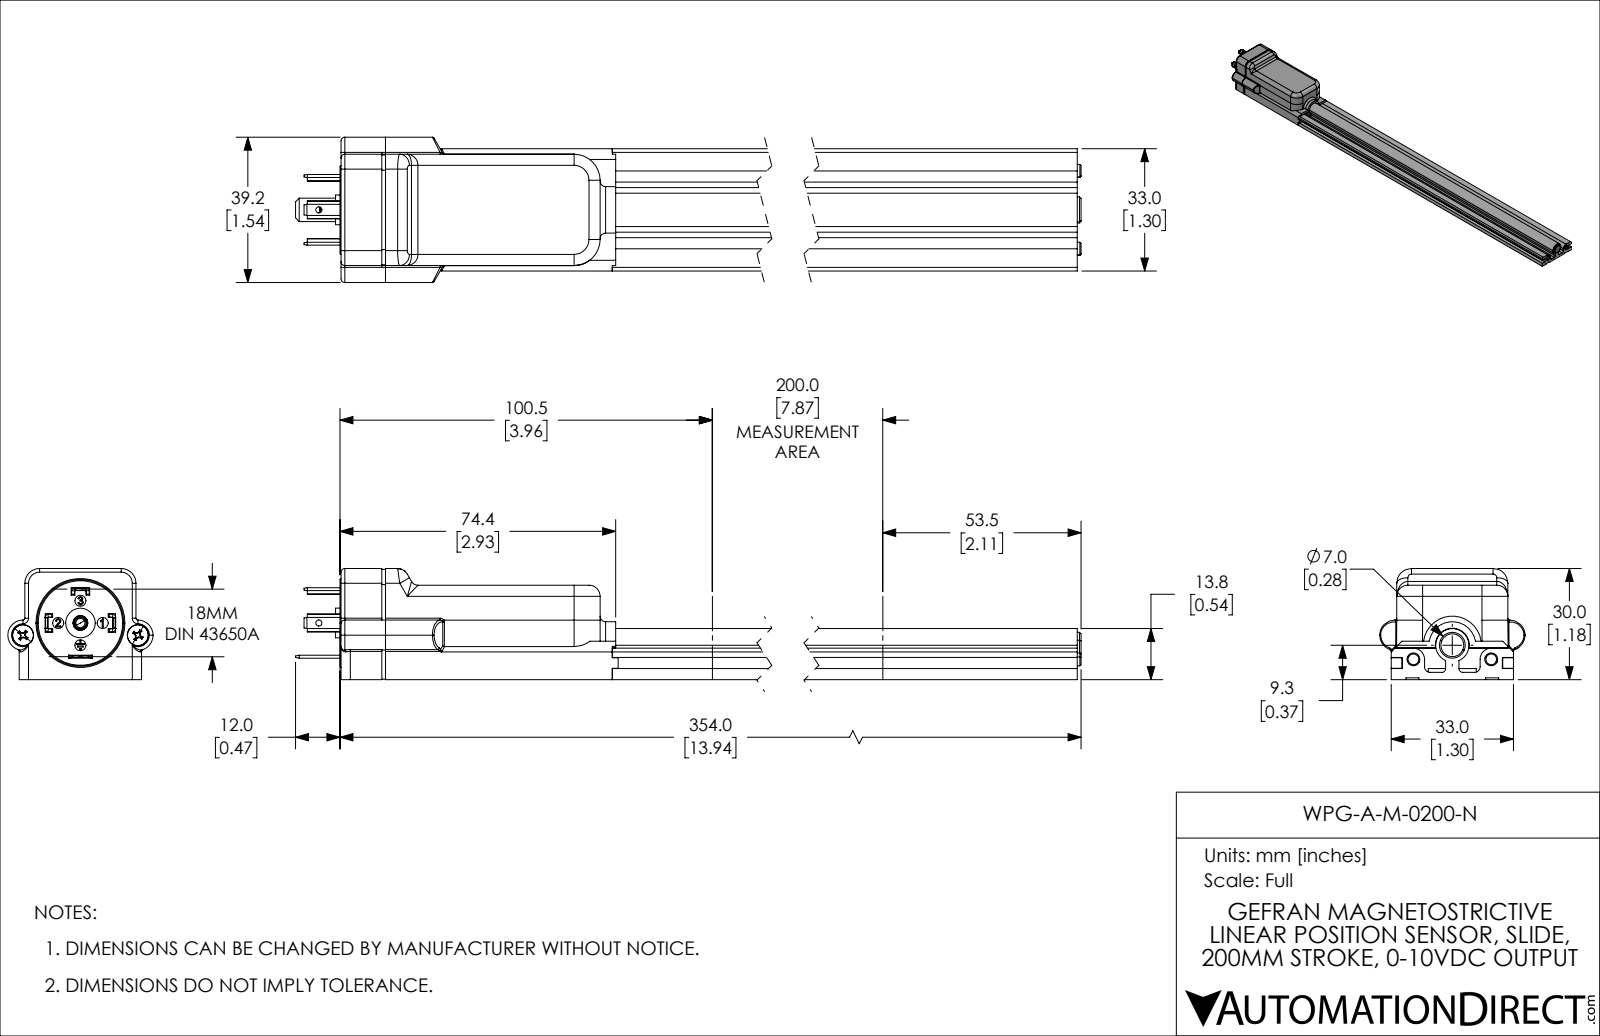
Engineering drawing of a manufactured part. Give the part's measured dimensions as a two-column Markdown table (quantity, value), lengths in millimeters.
| quantity | value |
| --- | --- |
| part name | WPG-A-M-0200-N |
| STEP written by | SolidWorks 2021 (CONFIG_CONTROL_DESIGN) |
| units | millimeters |
| bodies | 15 solids, 589 faces (371 planar, 139 cylindrical, 79 other) |
| overall size | 366 × 39.2 × 30 |
| volume | 124 954 mm³ |
| surface area | 54 056 mm² |
| round holes (diameter × count) | 3 × 5, 1.5 × 2, 1.65 × 2, 3.2 × 2, 5.7 × 2, 1.6 × 1, 2.5 × 1, 4 × 1 |
| round bosses / shafts (diameter × count) | 5.6 × 2, 3.5 × 2, 2.85 × 2, 9 × 1, 8 × 1, 7 × 1, 5.3 × 1, 3.94 × 1 |
| partial cylindrical surfaces (radius × count) | 0.5 × 8, 3 × 8, 0.85 × 6, 1 × 5, 0.8 × 4, 1.5 × 4, 4.1 × 4, 7 × 4 |
| main face-to-face distances | 3, 1, 1.5, 2.5, 5.5, 6, 8.5, 30, 22.5, 0.5 |
| hole center spacings | 6, 8.49, 10.06, 12, 12.3, 15.73, 15.85, 18.08 |
